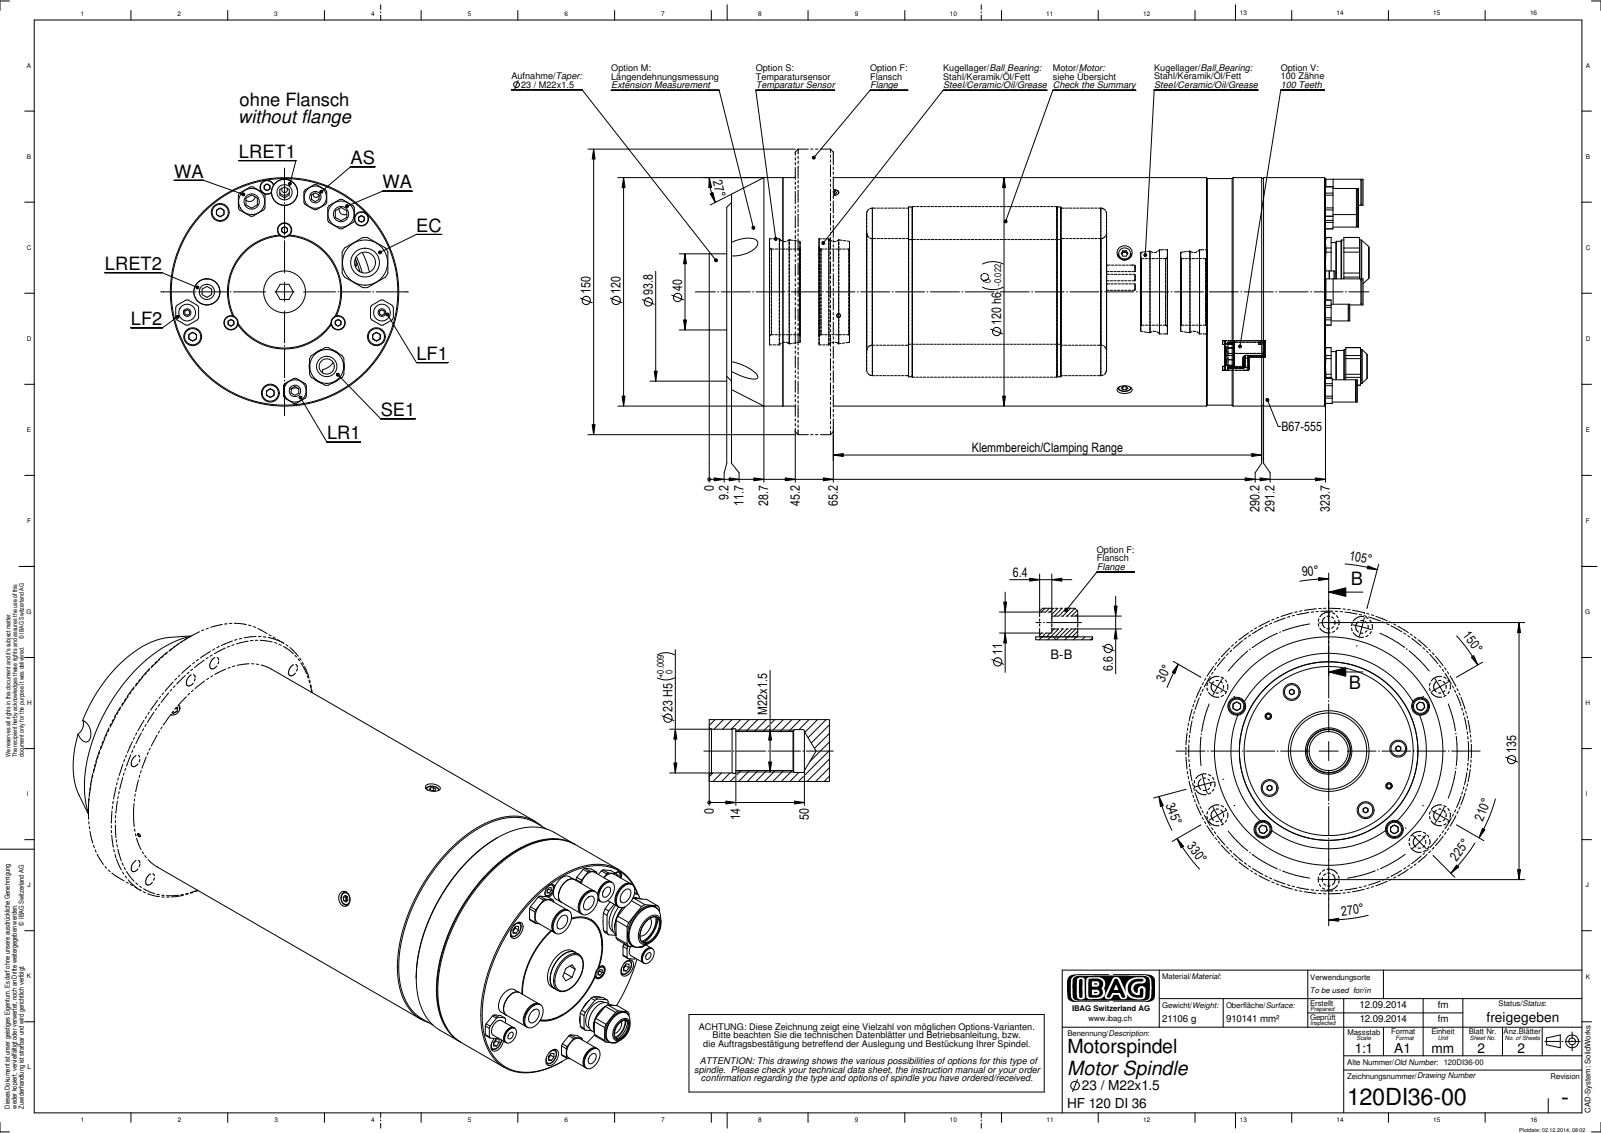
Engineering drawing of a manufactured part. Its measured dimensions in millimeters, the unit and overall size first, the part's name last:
Units: millimetres
Overall size (bounding box): 346.7 × 120 × 120
Round holes (diameter × count): ⌀8 ×9, ⌀9.4 ×8, ⌀5 ×7, ⌀4 ×2, ⌀6 ×2, ⌀7.4 ×2, ⌀7.5 ×2, ⌀6.8 ×1, ⌀10.7 ×1, ⌀11 ×1, ⌀15.1 ×1, ⌀16.2 ×1
Round bosses / shafts (diameter × count): ⌀13.7 ×4, ⌀7.64 ×4, ⌀13.7 ×2, ⌀11.7 ×2, ⌀8.8 ×2, ⌀7.92 ×2, ⌀120 ×1, ⌀119.2 ×1
Partial cylindrical surfaces — rounded edges, fillets, slot ends (radius × count): R6.6 ×4, R7.75 ×2, R3.75 ×1, R9.9 ×1, R13.2 ×1
Main face-to-face distances: 285, 29.5, 314.5, 282, 252.5, 32.5, 281, 251.5, 1, 33.5
Hole centre spacings: 53.7, 52.3, 79.49, 89.9, 101.11, 13, 21.4, 22.33
Bodies: 0 solids, 712 faces (330 planar, 254 cylindrical, 128 other)
Part name (STEP PRODUCT): 120DI36-00
STEP written by: SolidWorks 2014 (CONFIG_CONTROL_DESIGN)
